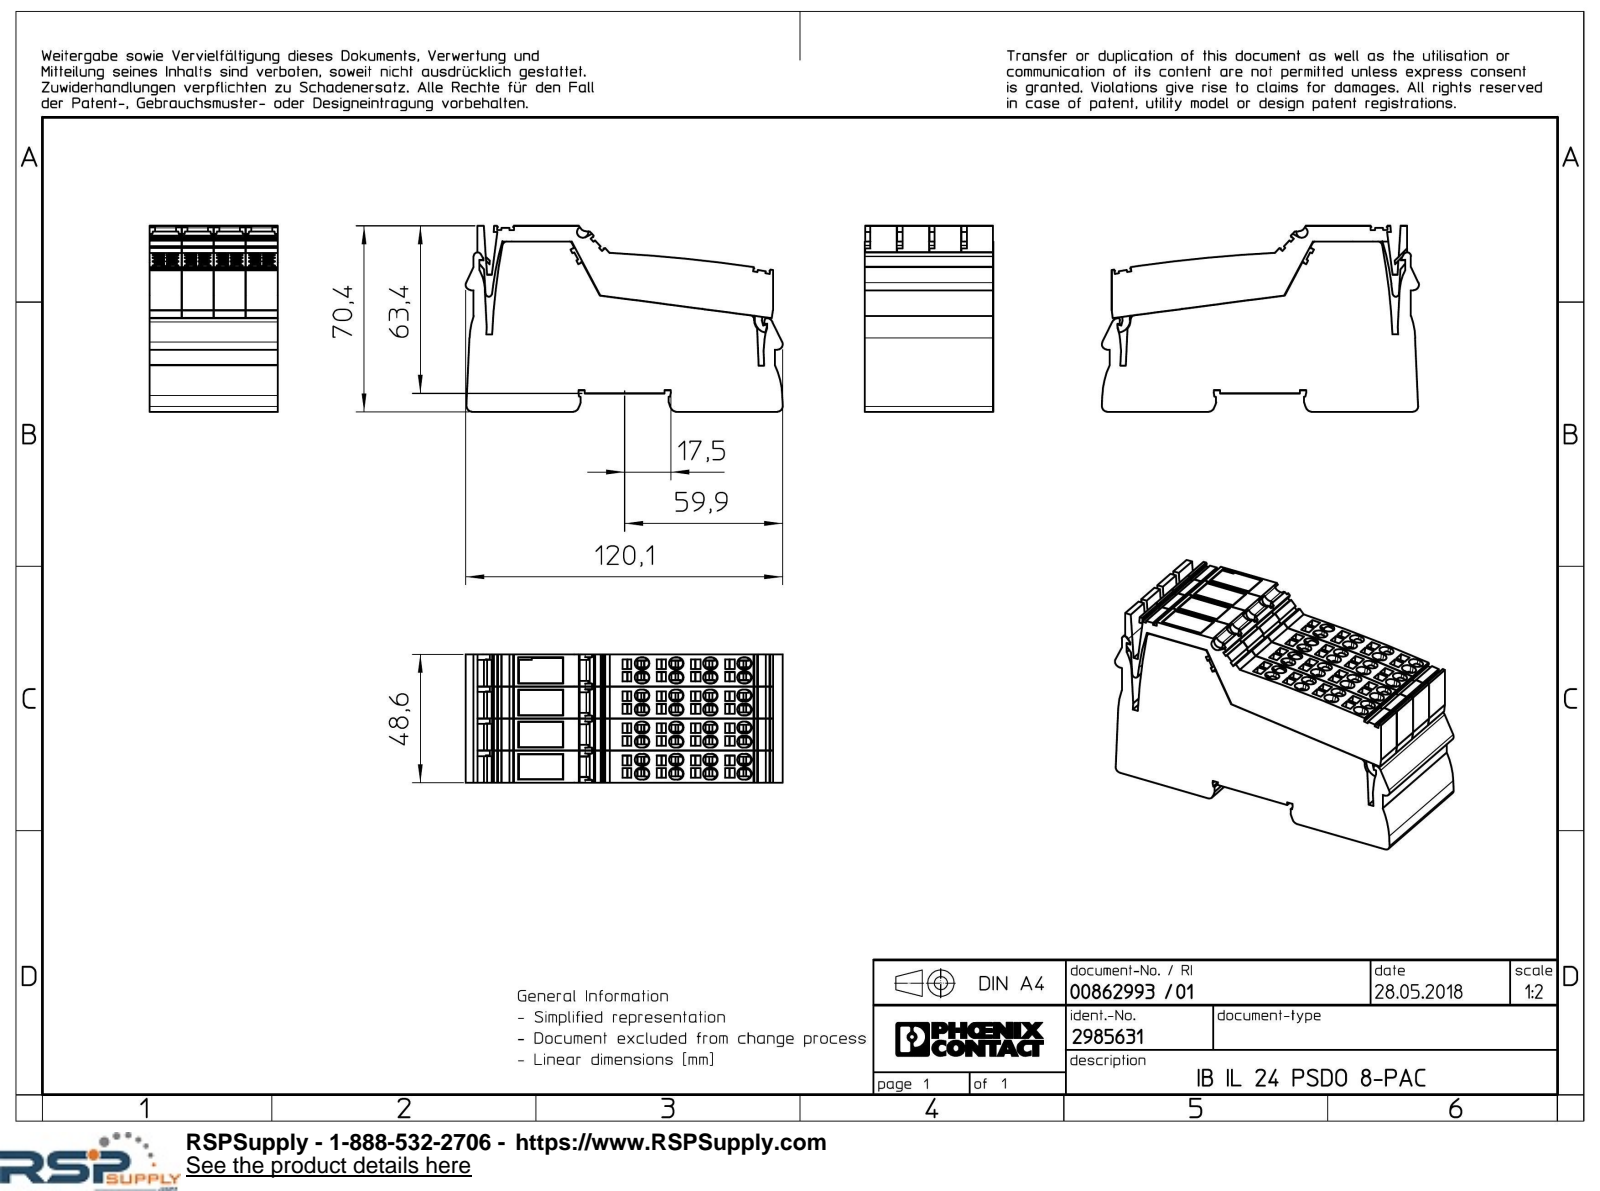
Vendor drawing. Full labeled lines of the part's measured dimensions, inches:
Part name (STEP PRODUCT): L_L_8_GEH_YE_1018-select; L_L_ST_YE_1018-select; L_L_LWL_PK-select; L_L_LWL_PK_AUSSEN-select (+1 more)
STEP written by: Creo Elements/Direct Modeling 20.1A 29-Sep-2018 (C) Parametric Technology GmbH (AUTOMOTIVE_DESIGN)
Units: inches
Bodies: 9 solids, 2113 faces (1820 planar, 181 cylindrical, 112 other)
Overall size (bounding box): 4.729 × 2.773 × 1.913
Volume: 19.58 in³ · Surface area: 126.3 in²
Round holes (diameter × count): ⌀0.047 ×24
Partial cylindrical surfaces — rounded edges, fillets, slot ends (radius × count): R0.089 ×64, R0.024 ×8, R0.079 ×6, R0.006 ×2, R0.067 ×2, R0.335 ×2, R0.374 ×2, R0.657 ×2
Main face-to-face distances: 0.478, 0.957, 0.472, 1.913, 0.951, 1.435, 0.484, 1.429, 1.023, 0.511
Hole centre spacings: 0.701, 0.478, 0.512, 0.546, 1.085, 0.189, 0.588, 0.841
